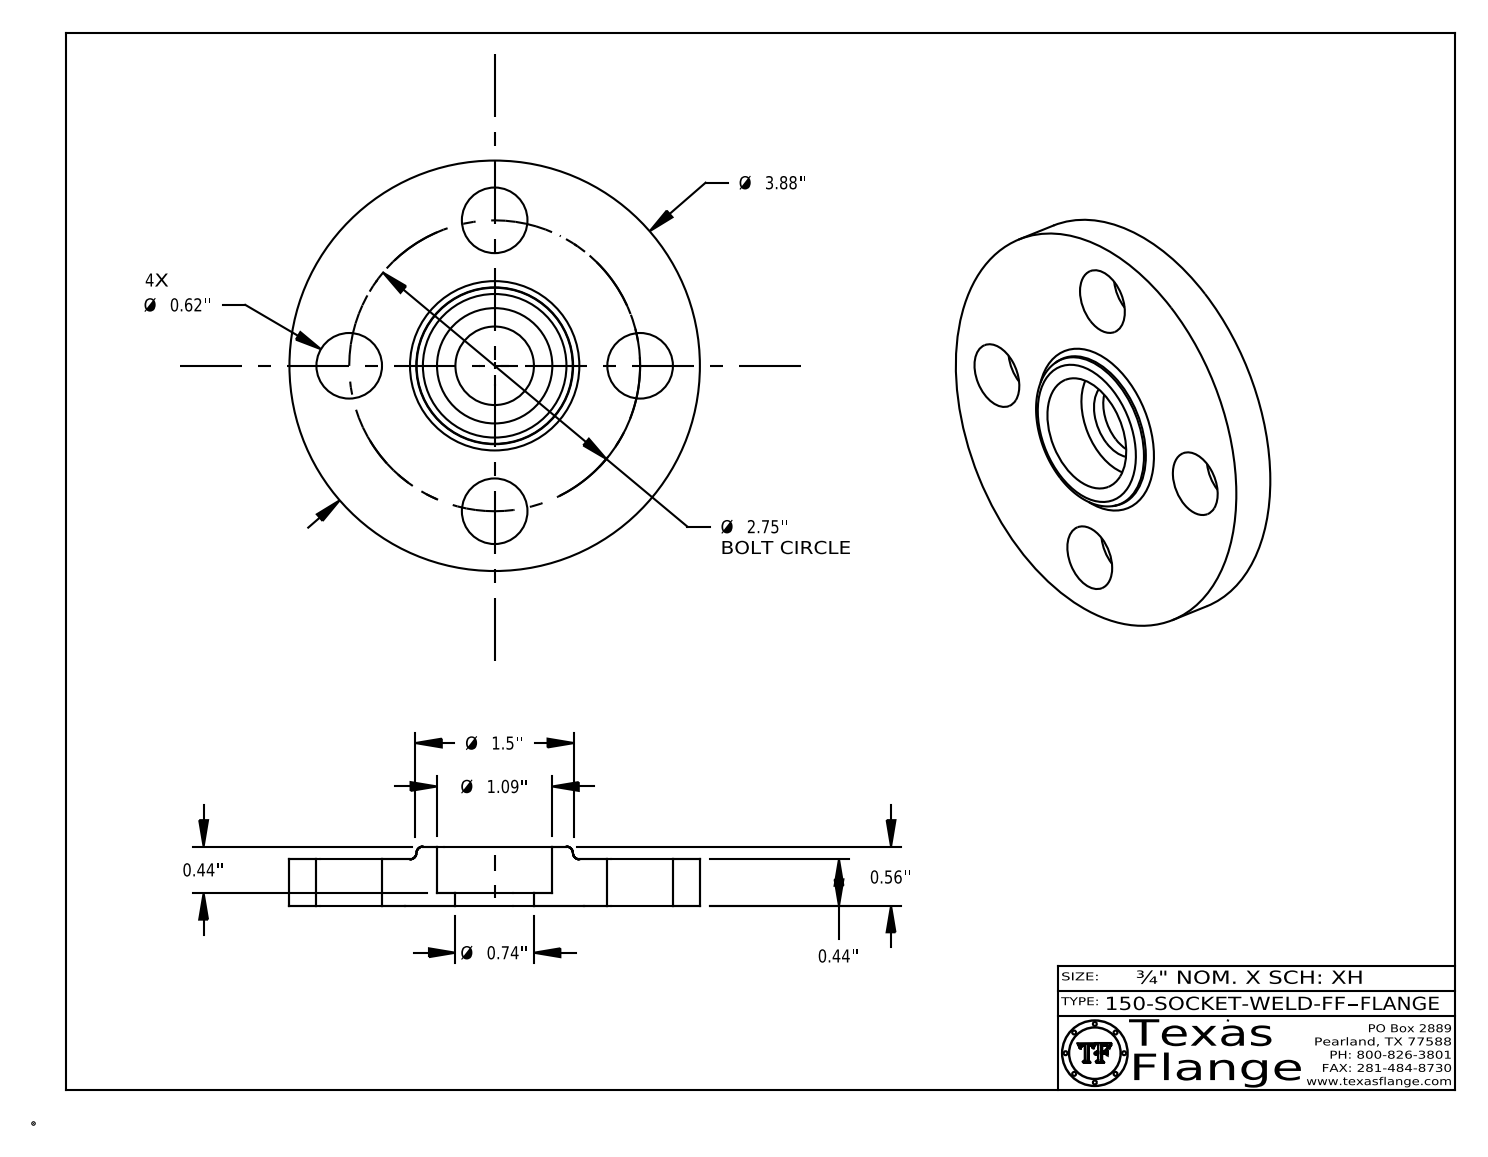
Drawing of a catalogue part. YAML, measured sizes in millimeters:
part_name: "150-SOCKET-WELD-FF"
step_written_by: "CATIA V5 STEP AP214 (AUTOMOTIVE_DESIGN)"
units: millimeters
bodies: {solids: 1, faces: 410, planar: 370, cylindrical: 34, other: 6}
overall_size: [98.6, 98.6, 14.2]
volume: 72330
surface_area: 20230
round_holes:
  - {diameter: 15.7, count: 4}
  - {diameter: 12.6, count: 1}
  - {diameter: 18.8, count: 1}
  - {diameter: 27.7, count: 1}
round_bosses_or_shafts:
  - {diameter: 0.8, count: 8}
  - {diameter: 98.6, count: 1}
  - {diameter: 9.9, count: 1}
face_to_face_distances: [11.2, 14.2, 3, 3, 8.1, 11.2, 10.8, 7.7, 0.4, 3.4]
hole_center_spacings: [34.9, 49.4, 26.7, 64.5, 69.9]
